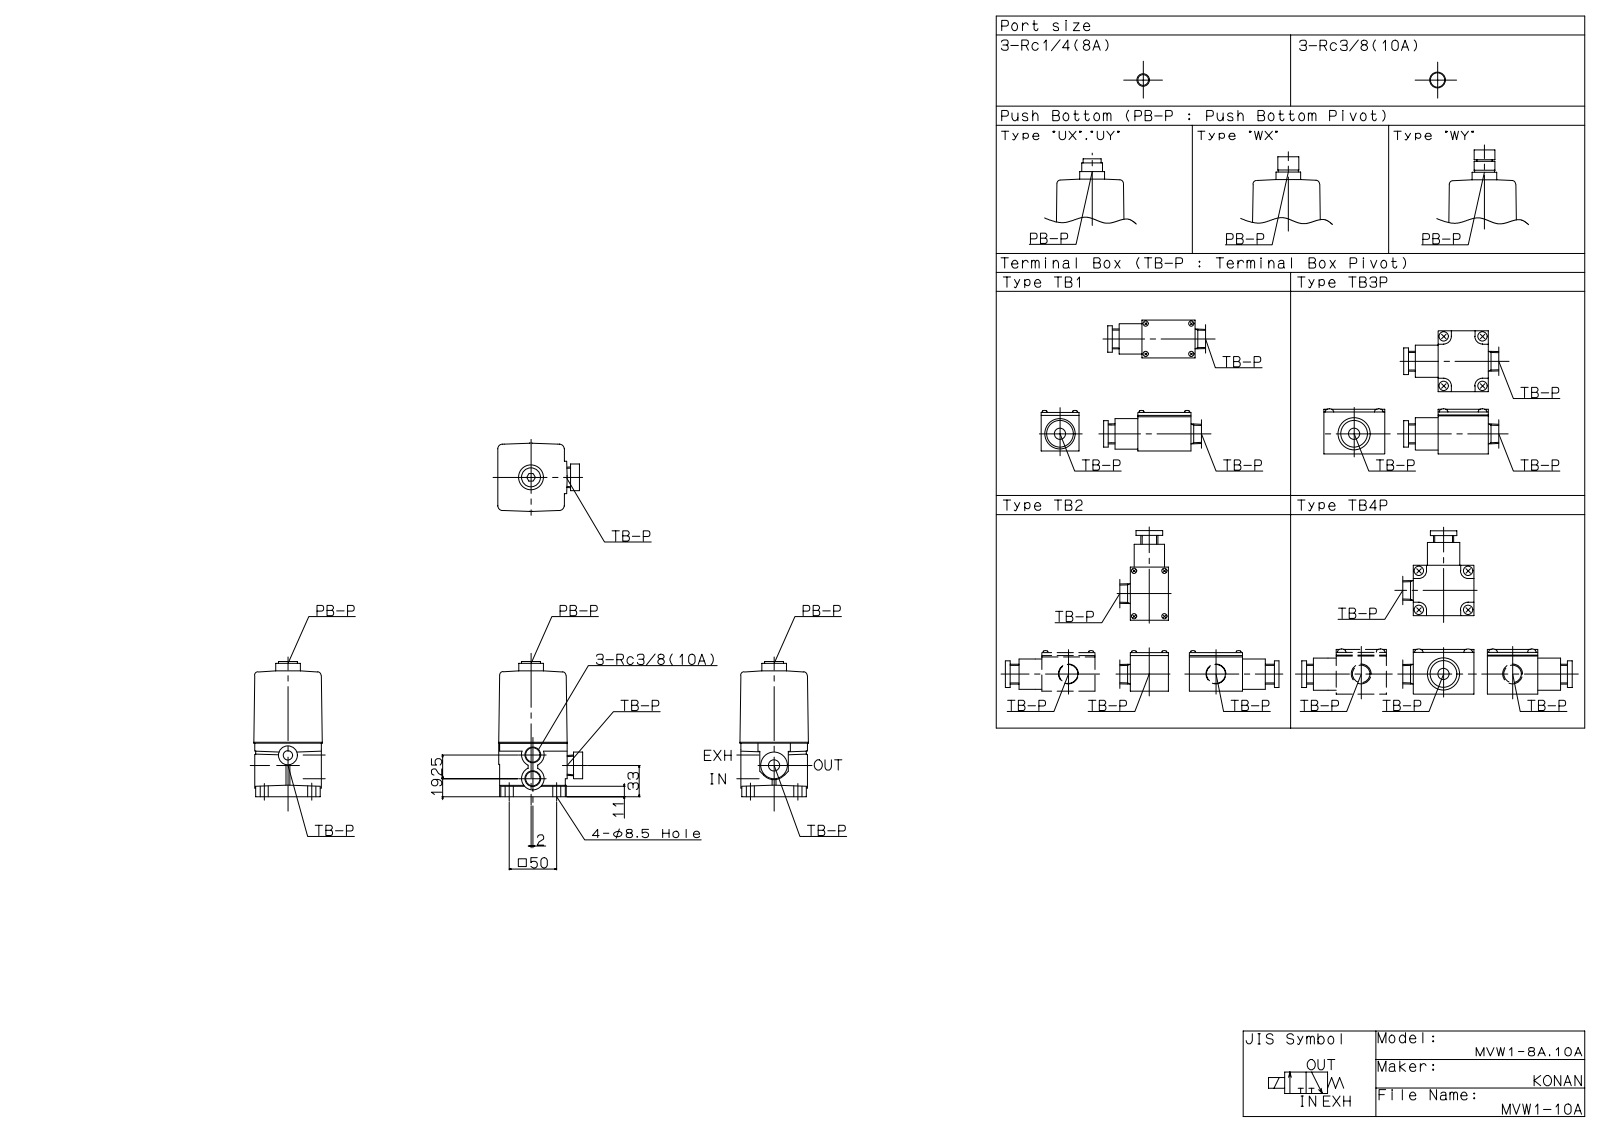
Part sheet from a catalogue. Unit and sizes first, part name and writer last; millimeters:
Units: millimetres
Overall size (bounding box): 142.5 × 88 × 70
Round holes (diameter × count): ⌀17.3 ×3
Round bosses / shafts (diameter × count): ⌀28 ×1, ⌀26 ×1, ⌀24 ×1, ⌀22 ×1, ⌀20 ×1
Partial cylindrical surfaces — rounded edges, fillets, slot ends (radius × count): R5 ×4, R8 ×4, R7 ×1, R10 ×1, R12 ×1, R14 ×1, R15 ×1
Main face-to-face distances: 70, 132.5, 48, 37, 11, 121.5, 72, 4, 84.5, 68
Hole centre spacings: 11, 14, 25
Volume: 557 188 mm³ · Surface area: 56 710 mm²
Bodies: 1 solid, 76 faces (40 planar, 36 cylindrical, 0 other)
Part name (STEP PRODUCT): MVW1-10A
STEP written by: SolidWorks 2023 (AUTOMOTIVE_DESIGN)
